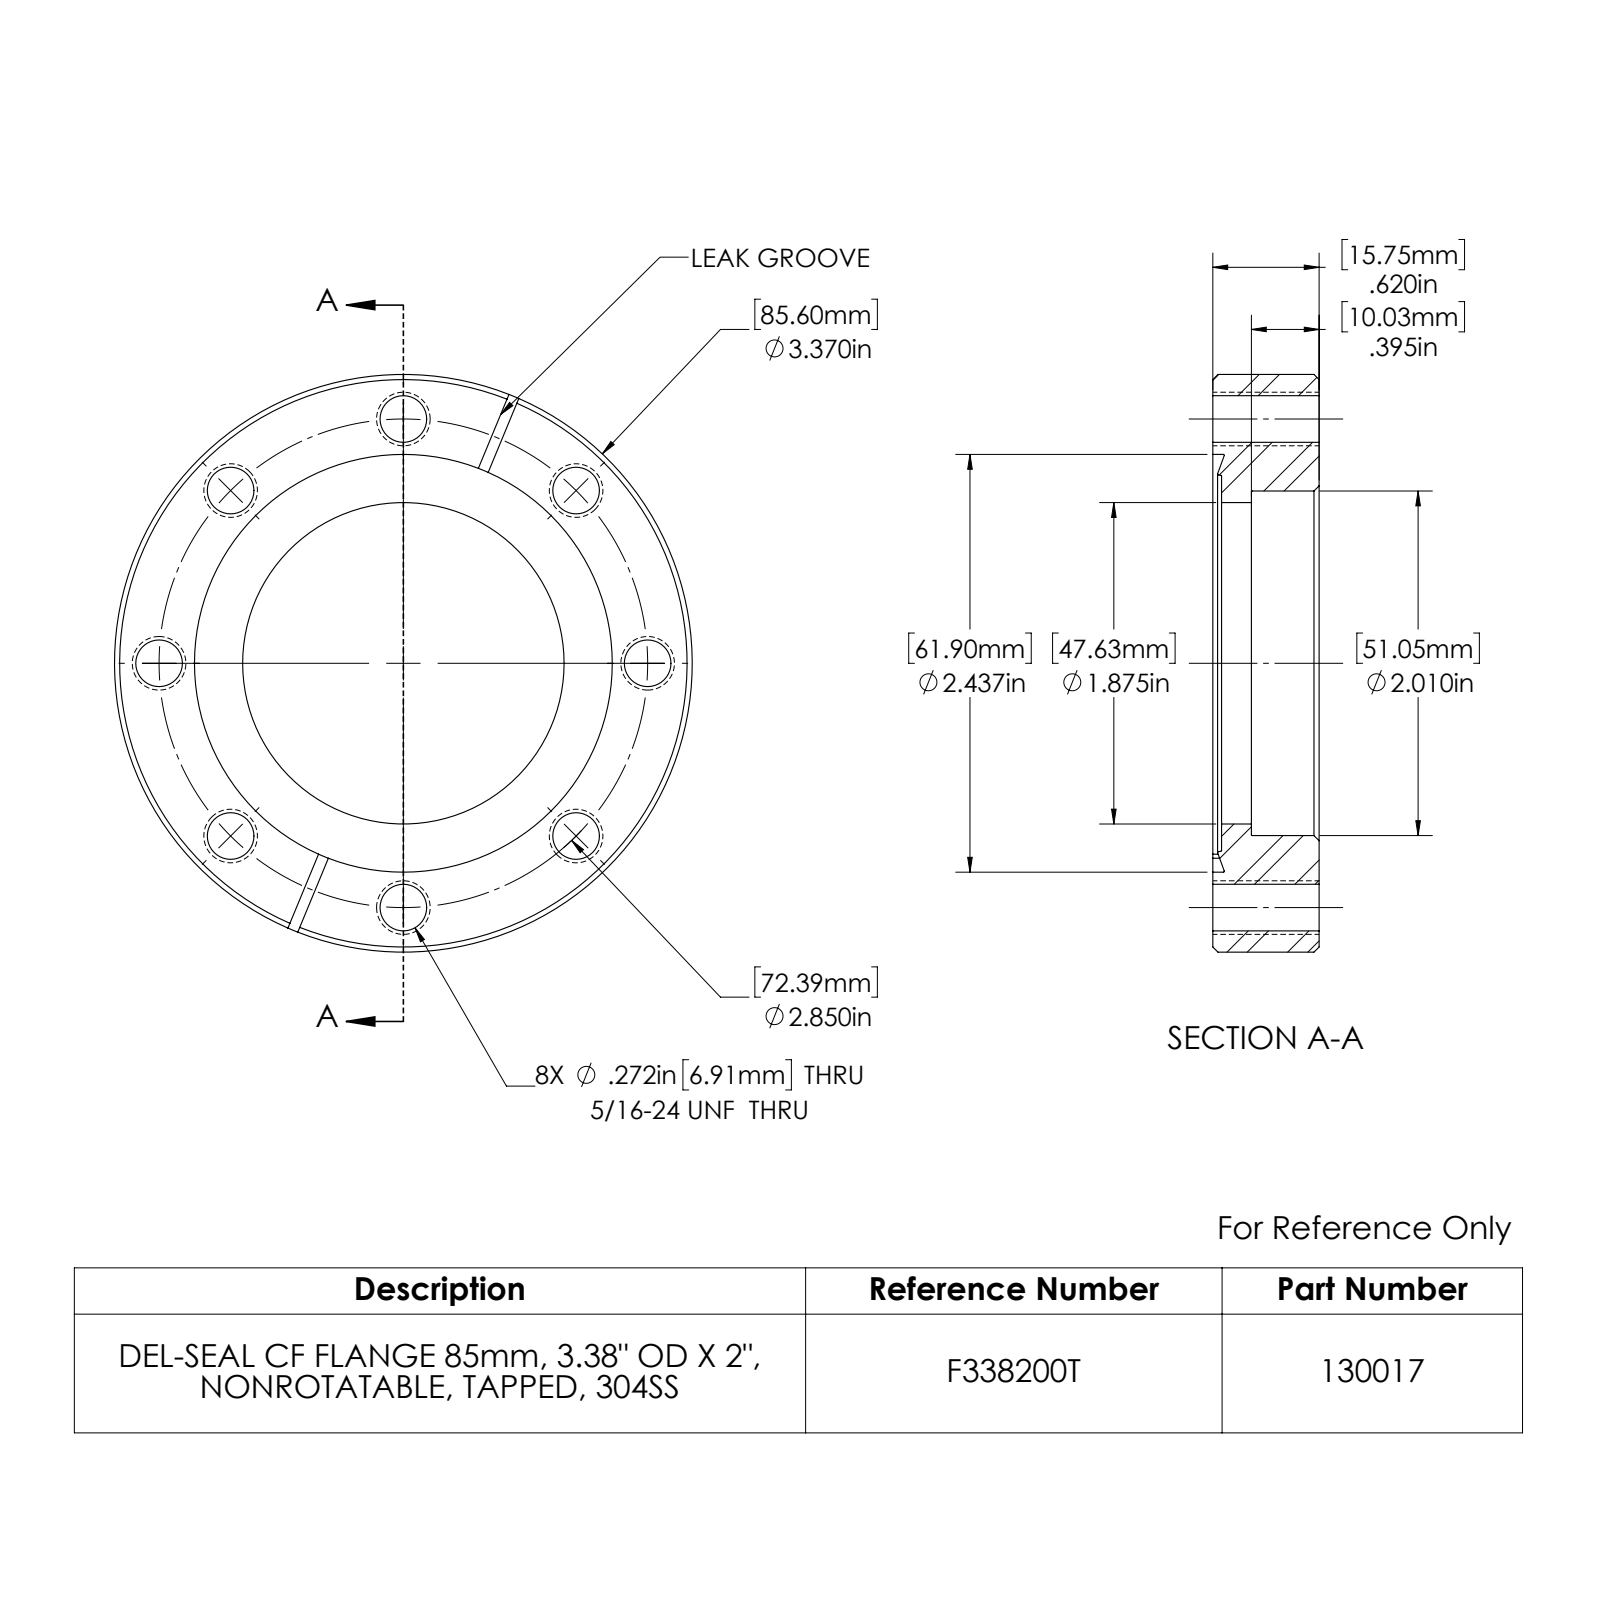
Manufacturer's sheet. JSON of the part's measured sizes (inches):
{"part_name": "130017", "step_written_by": "SolidWorks 2022 (AUTOMOTIVE_DESIGN)", "units": "inches", "bodies": {"solids": 1, "faces": 54, "planar": 11, "cylindrical": 24, "other": 19}, "overall_size": [3.37, 3.37, 0.62], "volume_in3": 3.258, "surface_area_in2": 25.96, "round_holes": [[0.272, 8], [1.875, 1], [2.01, 1], [2.437, 1]], "round_bosses_or_shafts": [[3.37, 1]], "face_to_face_distances": [0.62, 0.051, 0.569, 0.225, 0.174, 0.395, 0.052, 0.173, 0.568, 0.062], "hole_center_spacings": [1.091, 2.633, 1.425, 1.425, 2.015, 2.015, 2.85, 2.85]}
